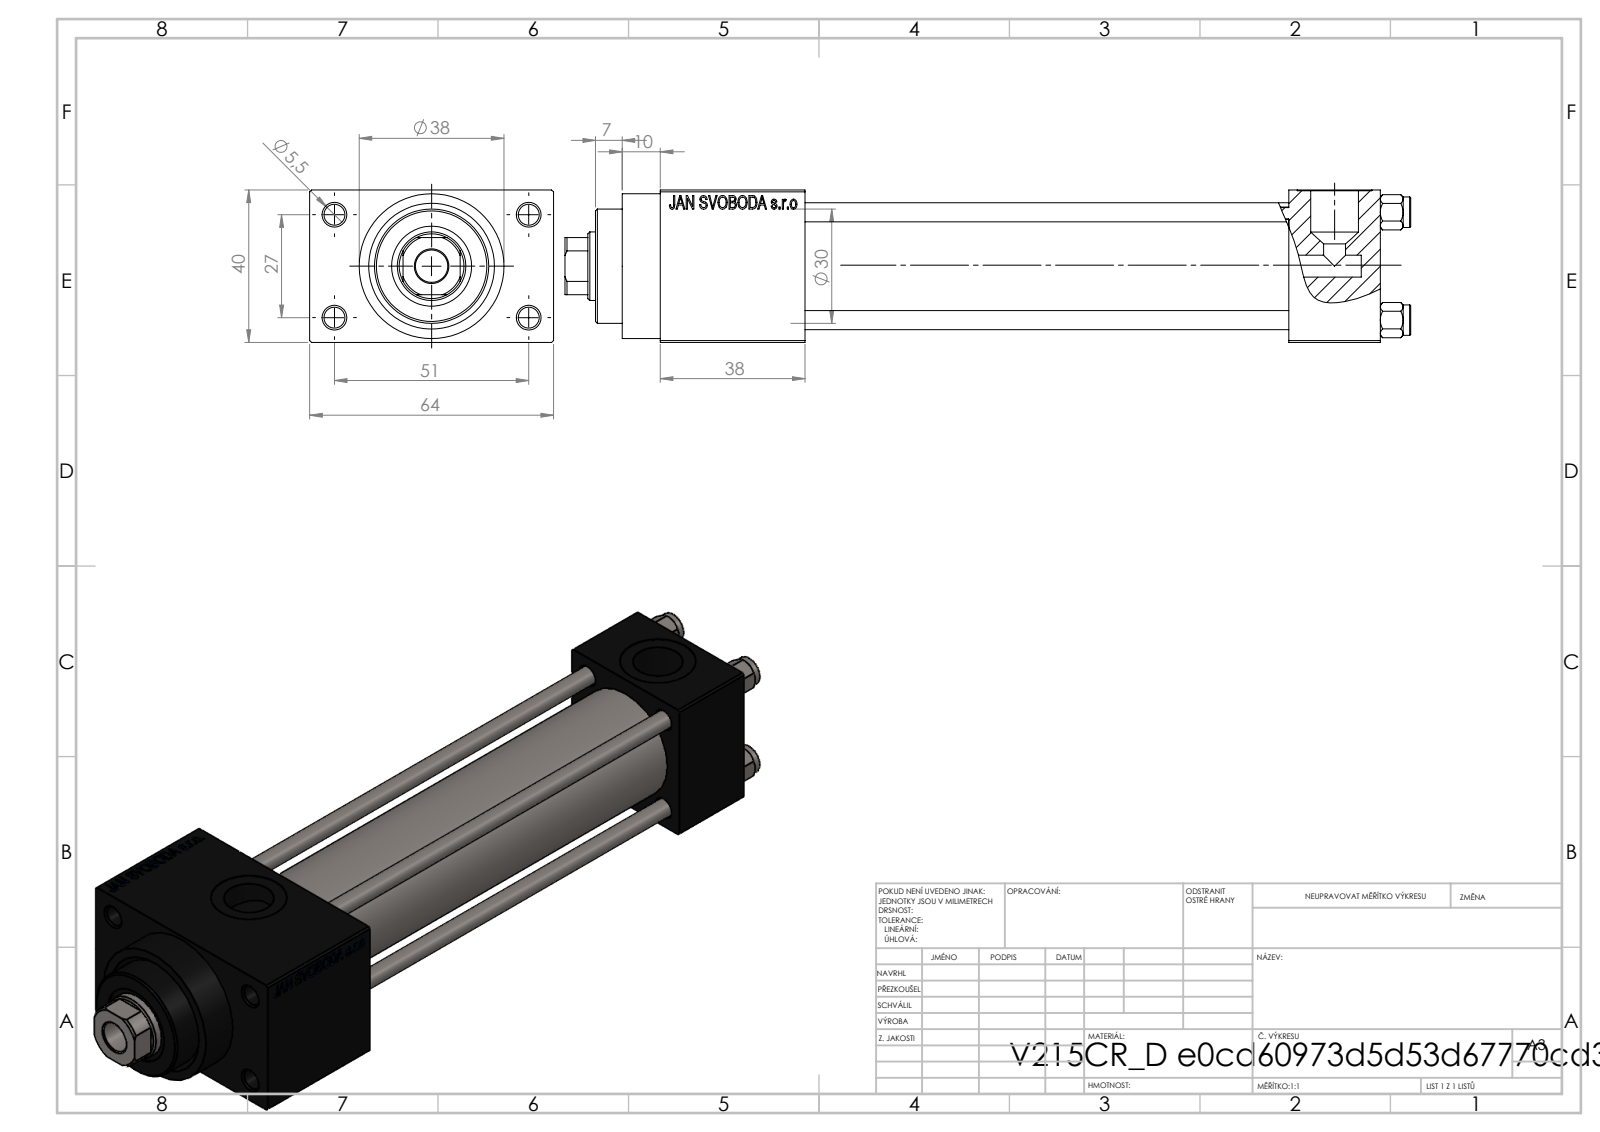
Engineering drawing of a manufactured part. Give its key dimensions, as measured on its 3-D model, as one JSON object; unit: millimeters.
{"part_name": "V215CR_D_Body; NUT_M5_D; V215CR_D_TYCINKA; V215_VC_A (+1 more)", "step_written_by": "SolidWorks 2019 (CONFIG_CONTROL_DESIGN)", "units": "millimeters", "bodies": {"solids": 11, "faces": 1102, "planar": 495, "cylindrical": 87, "other": 520}, "overall_size": [222, 64, 40], "volume_mm3": 228426, "surface_area_mm2": 87759, "round_holes": [[5, 4], [5.5, 4], [20, 3], [7, 2], [13.16, 2], [8.5, 1], [18, 1], [21, 1], [25, 1], [30, 1]], "round_bosses_or_shafts": [[8, 4], [38, 1], [31, 1]], "partial_cylinders_radius": [[8.5, 1]], "face_to_face_distances": [40, 12, 52, 127, 24, 151, 64, 38, 189, 165], "hole_center_spacings": [11.37, 20.01, 28.3, 28.85, 29.89, 39.66, 48.34, 27]}
